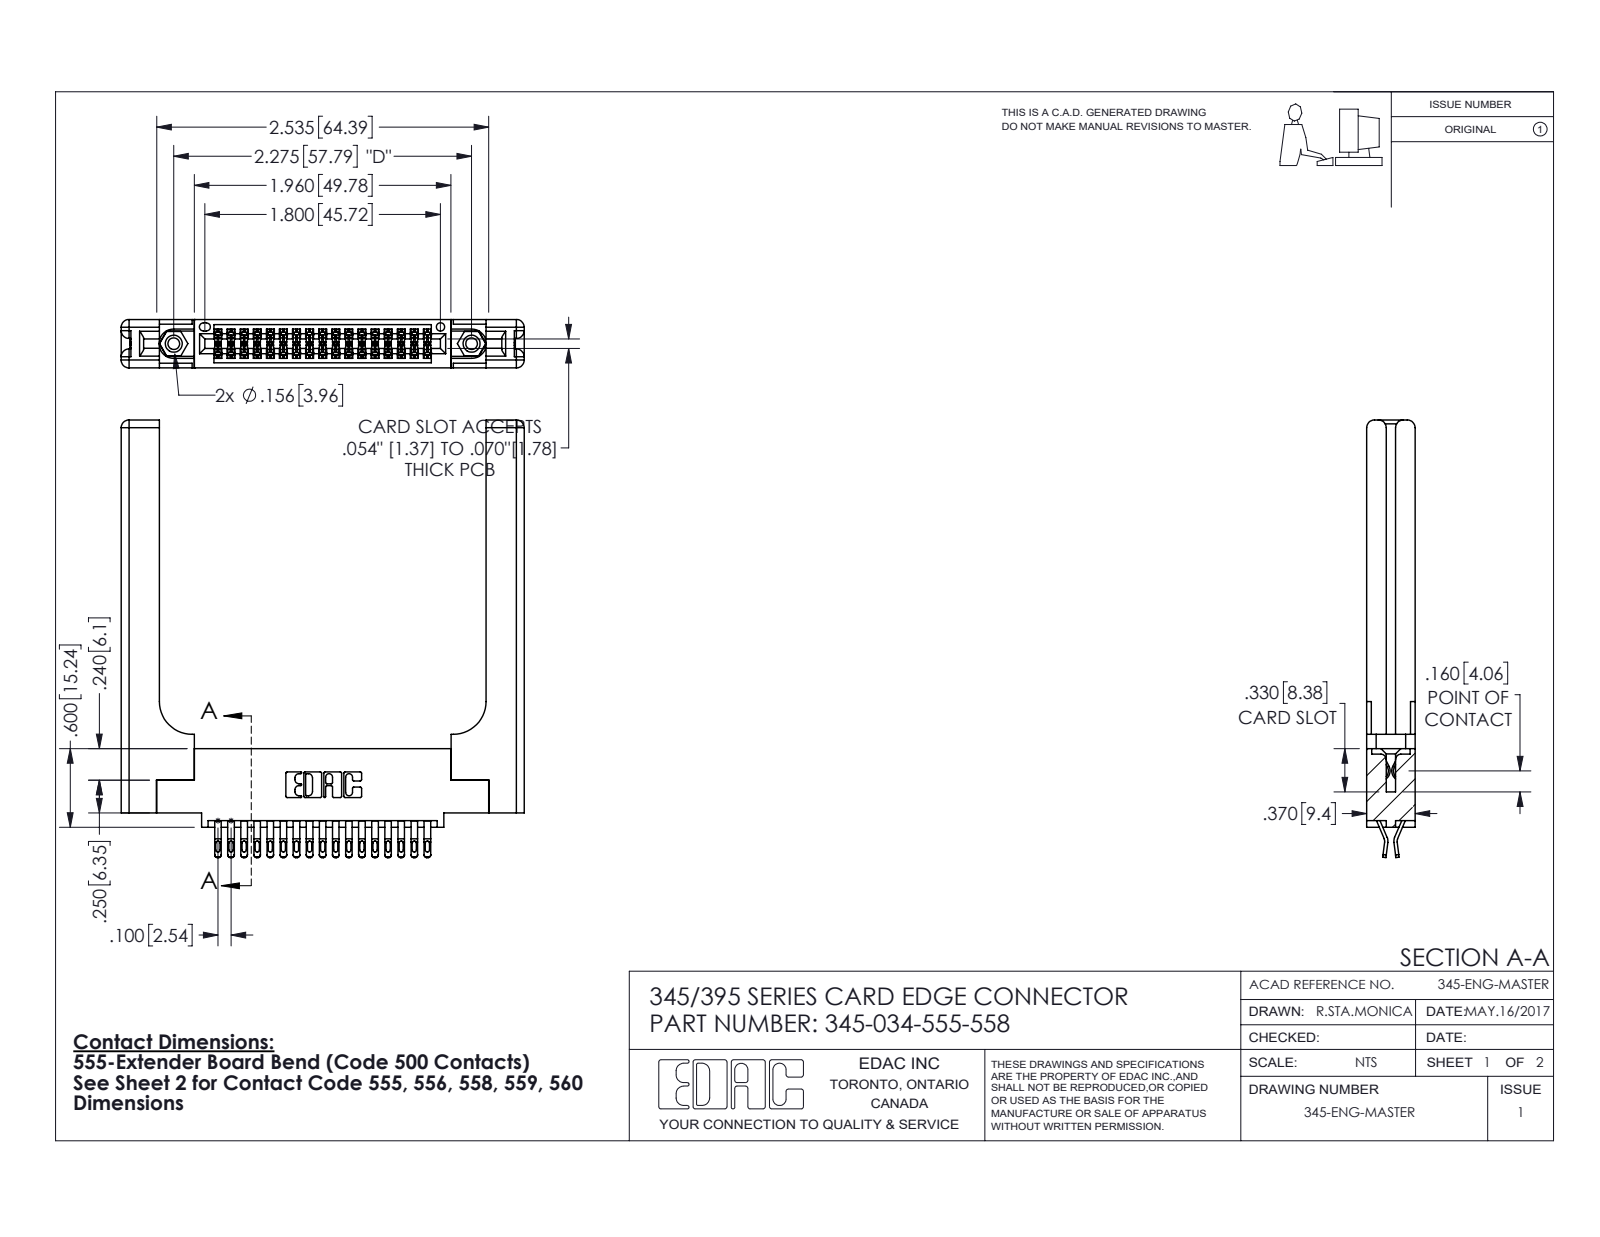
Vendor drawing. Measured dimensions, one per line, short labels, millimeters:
name: 345 Part_0.110 Offset - 0.156 Dia-TH; 345-034-555-558; 345-220-058_345-220-058; 345-292-001_555 Tail (+1 more)
written by: SolidWorks 2016 (CONFIG_CONTROL_DESIGN)
unit: mm
bodies: 39 solids, 2290 faces (1286 planar, 944 cylindrical, 60 other)
size: 84.9 × 78.2 × 9.4
volume: 15 900 mm³; area: 15 940 mm²
holes: 2× ⌀2.3, 2× ⌀3.2, 2× ⌀4, 1× ⌀1.6
bosses: 2× ⌀3.9
rounds: 85× R0.4, 68× R0.5, 51× R0.2, 22× R0.3, 16× R1.5, 6× R0.2, 6× R0.8, 3× R0.7
face distances: 9.4, 1.8, 7.6, 3.8, 3.8, 2, 5.6, 0.6, 5.7, 2.5
hole spacings: 6.9, 51.8, 57.8
